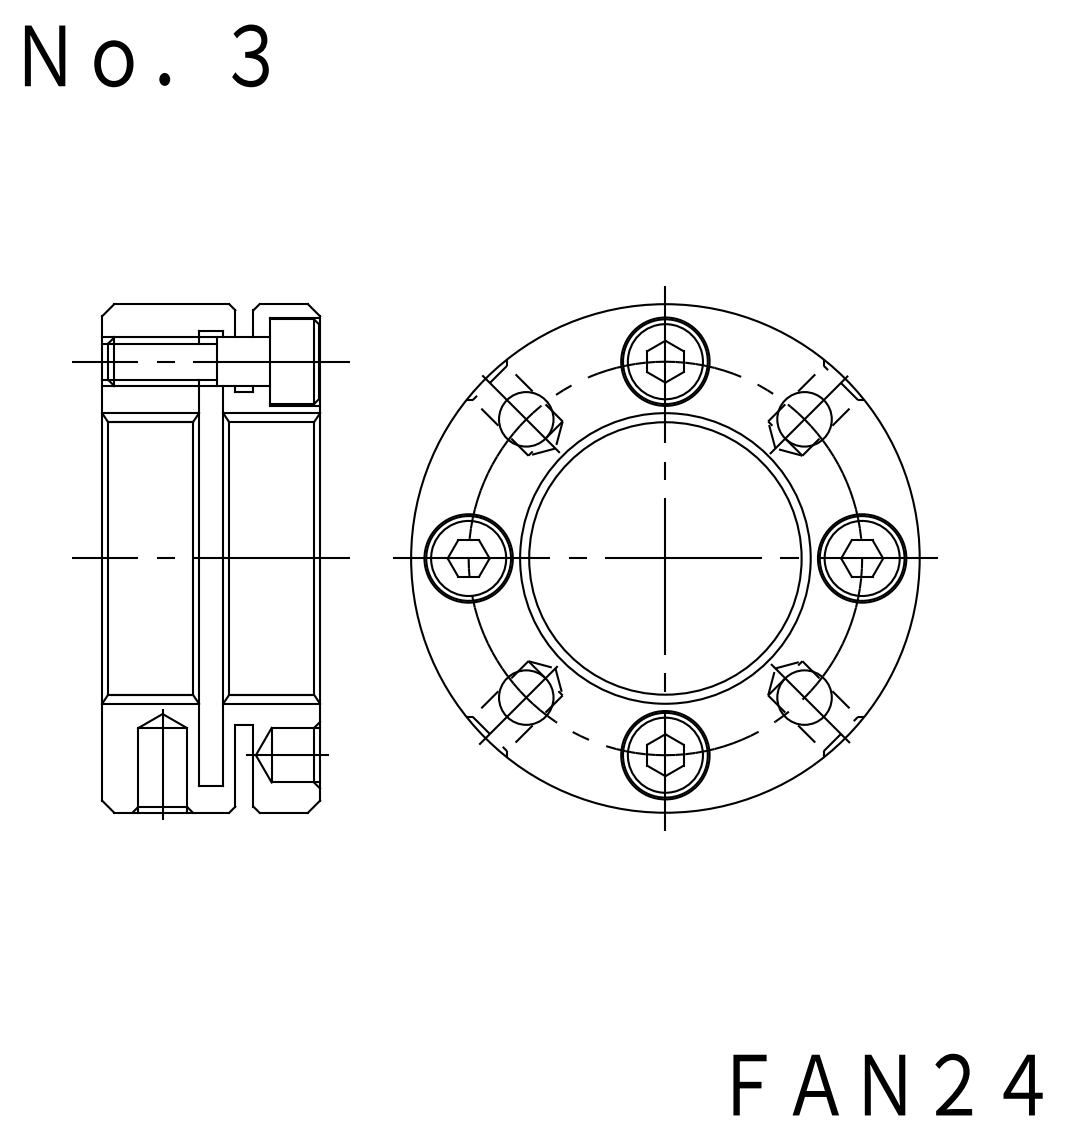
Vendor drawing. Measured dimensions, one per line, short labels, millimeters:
name: FKD FAN24; M4X12_default
written by: SolidWorks 2012 (CONFIG_CONTROL_DESIGN)
unit: mm
bodies: 5 solids, 142 faces (50 planar, 76 cylindrical, 16 other)
size: 42 × 42 × 18
volume: 13 779 mm³; area: 10 899 mm²
holes: 4× ⌀3.24, 4× ⌀4.3, 4× ⌀4.5, 4× ⌀7.3, 2× ⌀4, 1× ⌀24, 1× ⌀37.5
bosses: 4× ⌀7, 4× ⌀4, 1× ⌀42, 1× ⌀27.5
face distances: 8, 10, 11, 12.5, 1.5, 18, 7, 5.5, 2, 3
hole spacings: 12.44, 16.25, 22.98, 30.03, 32.5
